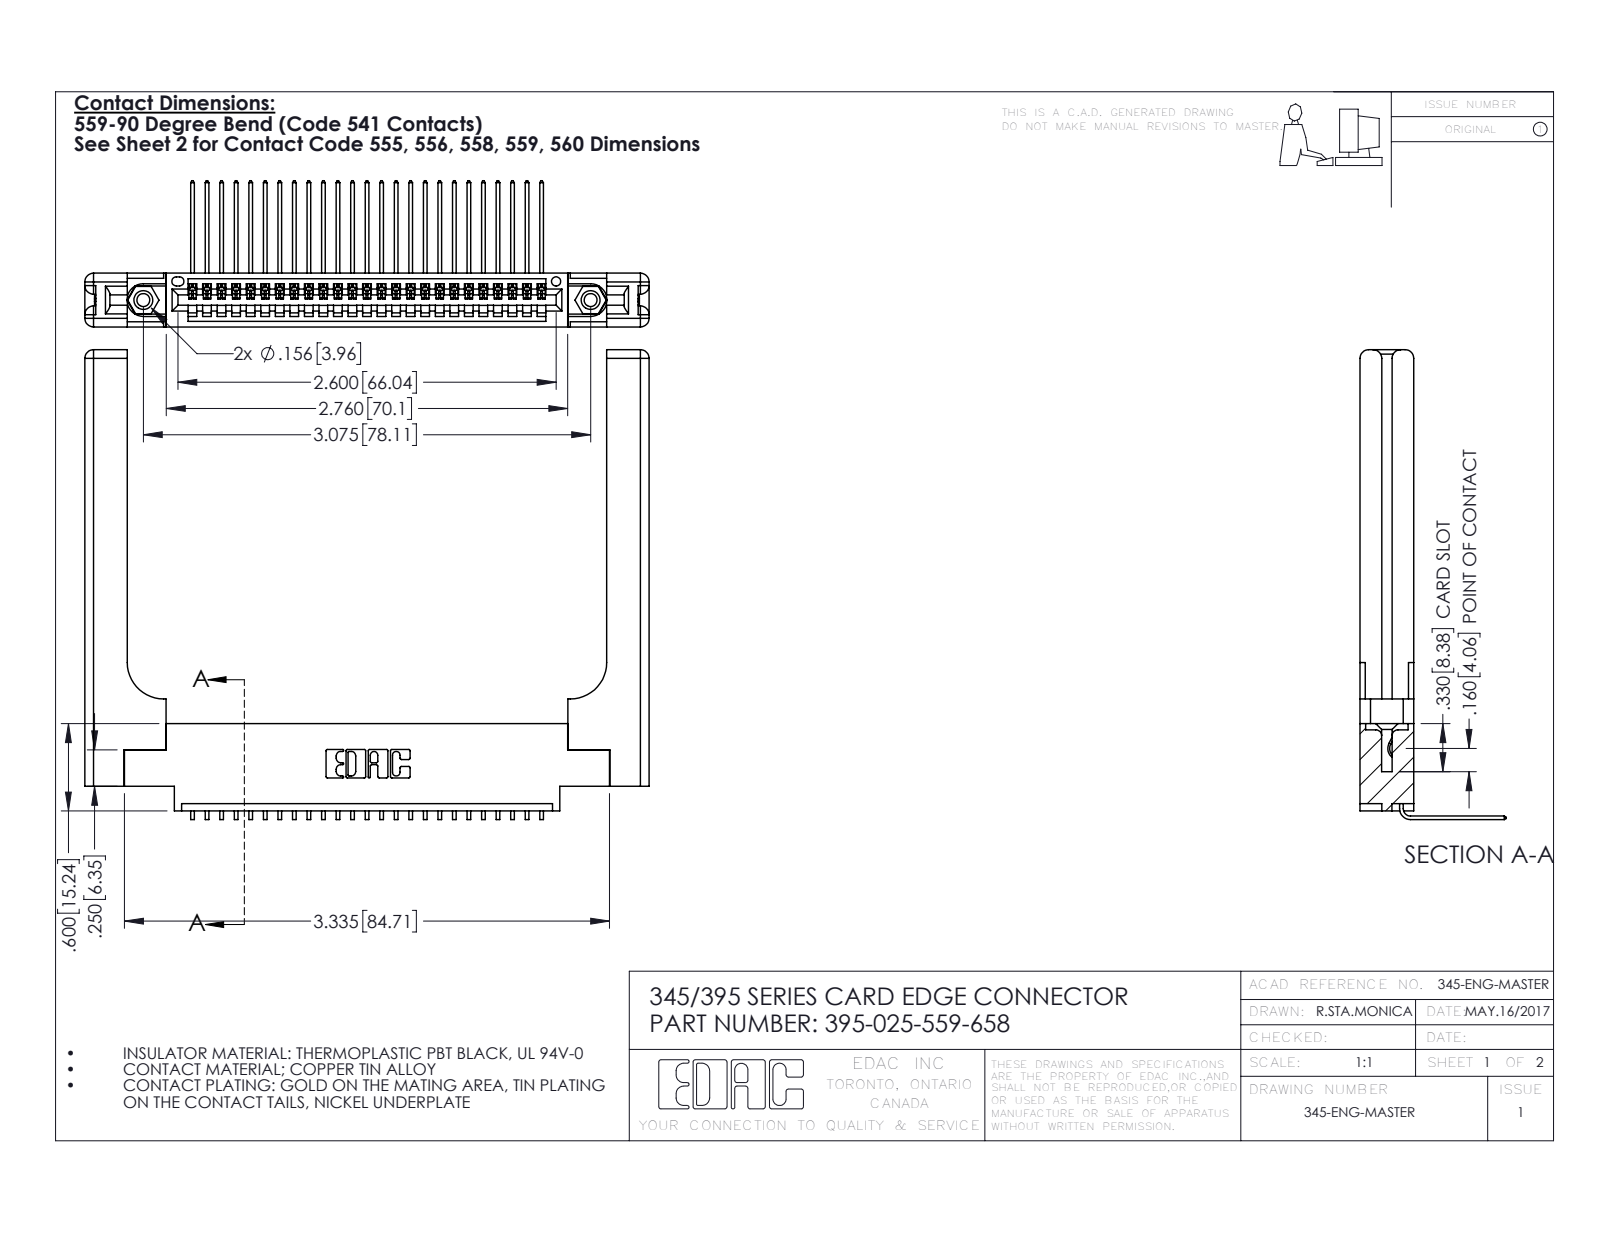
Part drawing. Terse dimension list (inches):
name: 345-250-001_345-250-001-102; 345 Part_0.170 Offset - 0.156 Dia-TH; 395-025-559-658; 345-220-058_345-220-058 (+1 more)
written by: SolidWorks 2016 (CONFIG_CONTROL_DESIGN)
unit: in
bodies: 30 solids, 1886 faces (1282 planar, 544 cylindrical, 60 other)
size: 3.879 × 3.229 × 1.005
volume: 1.08 in³; area: 27.75 in²
holes: 2× ⌀0.089, 2× ⌀0.125, 2× ⌀0.156, 1× ⌀0.064
bosses: 2× ⌀0.155
rounds: 50× R0.006, 22× R0.01, 16× R0.06, 6× R0.007, 6× R0.031, 3× R0.026, 2× R0.03, 2× R0.031
face distances: 0.37, 0.072, 0.298, 0.148, 0.15, 0.077, 0.22, 0.098, 0.272, 0.025
hole spacings: 0.27, 2.84, 3.075
